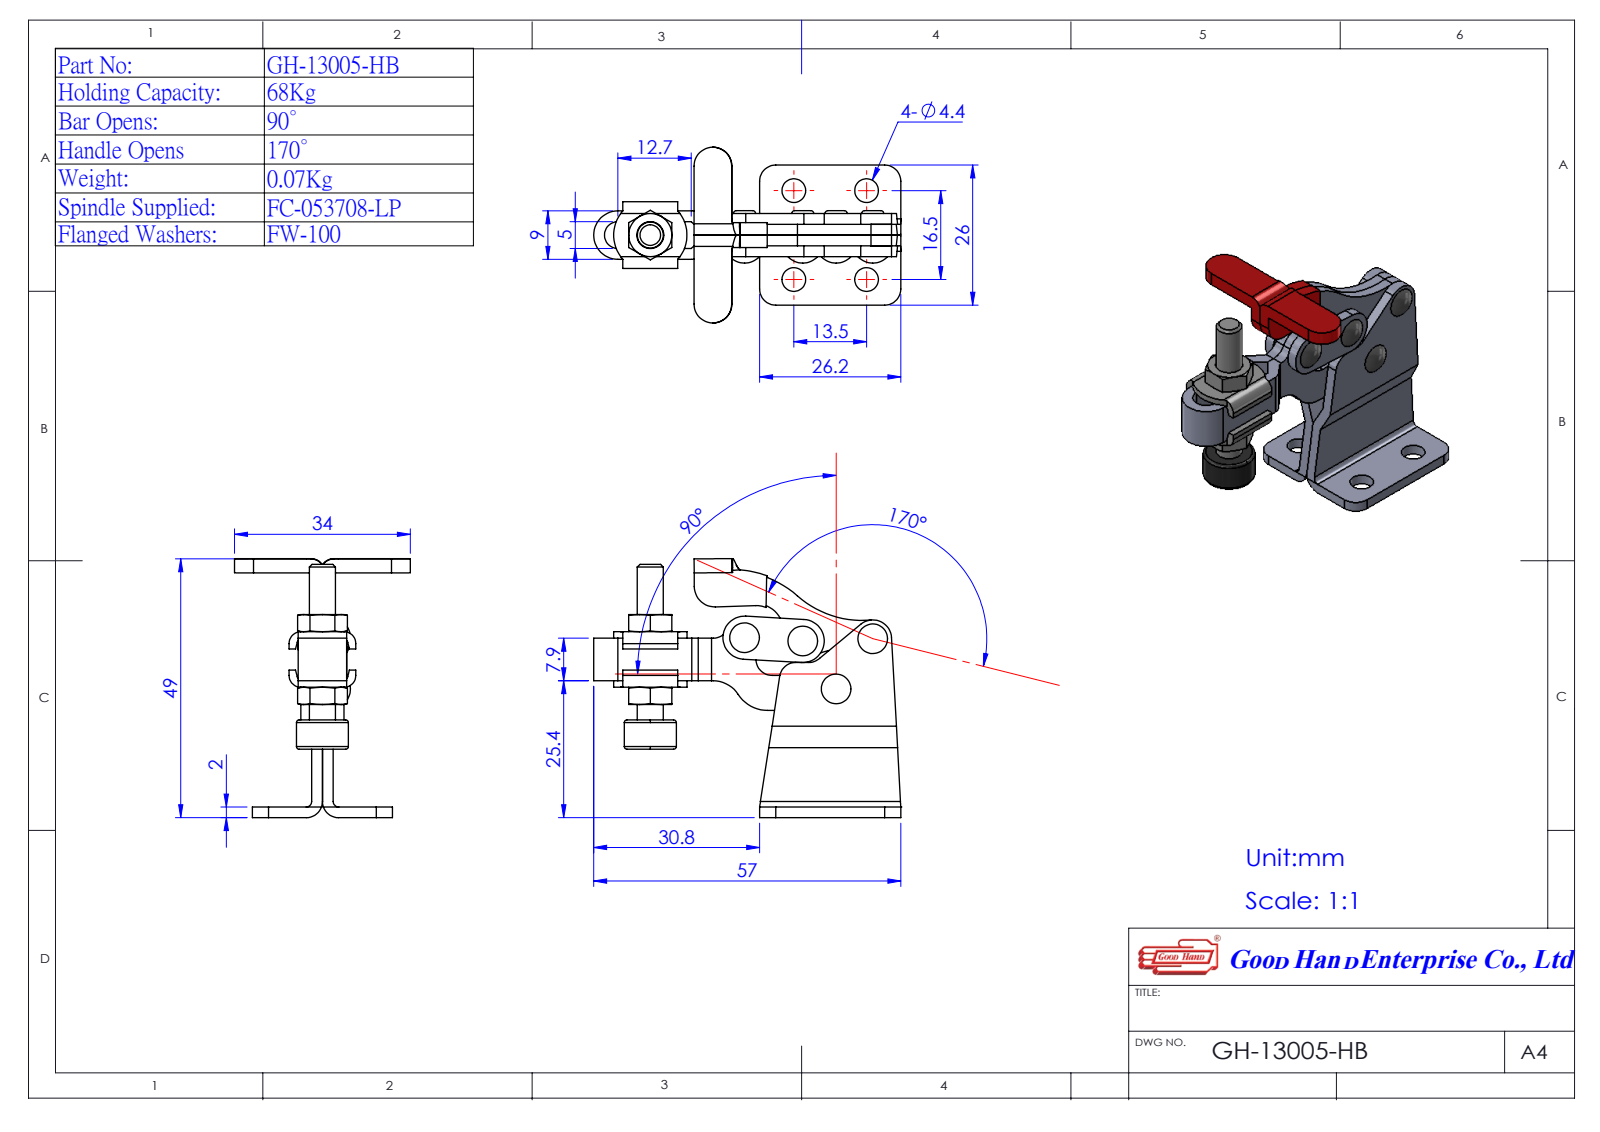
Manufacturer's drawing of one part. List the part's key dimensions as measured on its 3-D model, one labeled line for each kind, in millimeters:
Part name (STEP PRODUCT): Group2^GH-13005-HB(簡化)-1; Group7^GH-13005-HB(簡化)-1; 11300501-2^GH-13005-HB(簡化)-1; 11300508-1^GH-13005-HB(簡化)-1 (+2 more)
STEP written by: SolidWorks 2016 (AUTOMOTIVE_DESIGN)
Units: millimetres
Bodies: 6 solids, 275 faces (127 planar, 104 cylindrical, 44 other)
Overall size (bounding box): 57 × 48.39 × 33
Volume: 9 762 mm³ · Surface area: 11 313 mm²
Round holes (diameter × count): ⌀2.5 ×4, ⌀4.4 ×4
Round bosses / shafts (diameter × count): ⌀9.65 ×1, ⌀5 ×1
Partial cylindrical surfaces — rounded edges, fillets, slot ends (radius × count): R1 ×8, R3 ×6, R2.2 ×4, R3.5 ×4, R4 ×4, R1.01 ×2, R1.5 ×2, R1.7 ×2
Main face-to-face distances: 2, 4, 0.5, 6, 0.49, 6.5, 8, 1.5, 4.5, 8.5
Hole centre spacings: 10.83, 13.5, 16.5, 21.32, 11.52, 13, 19.47, 23.8
